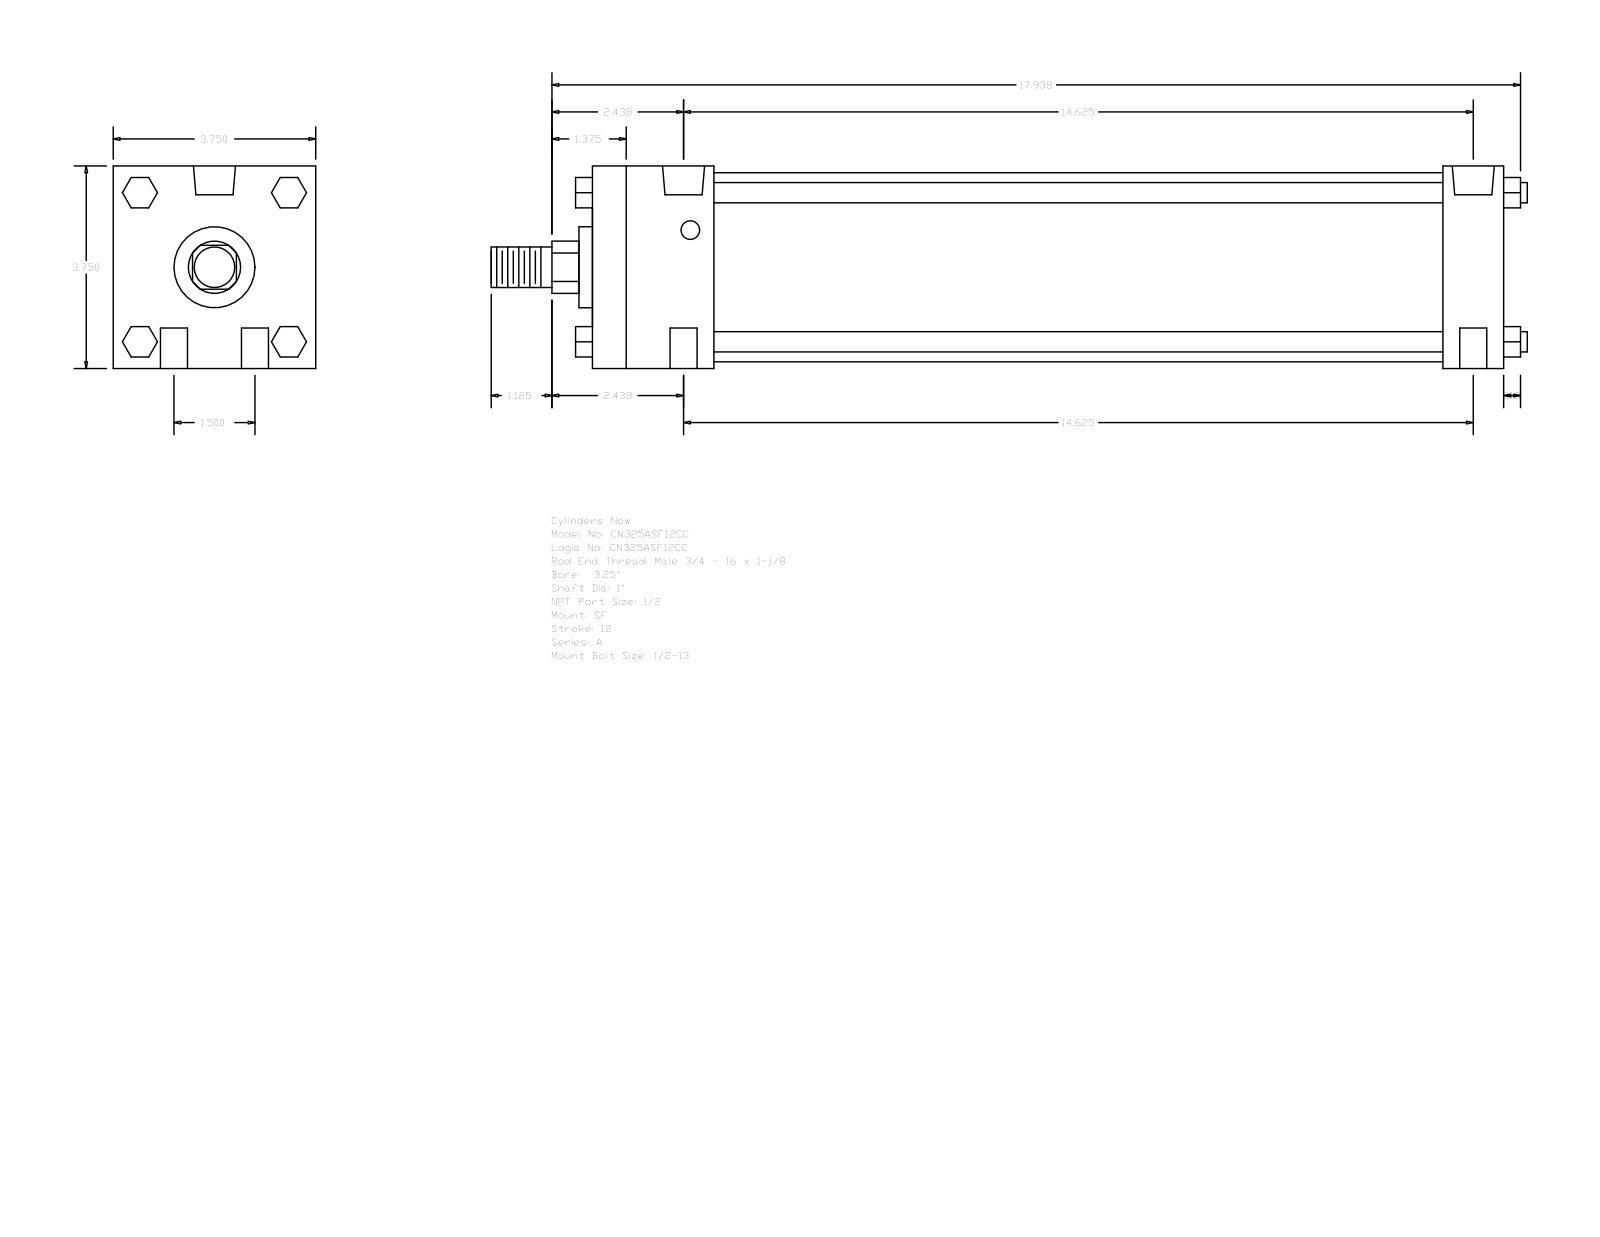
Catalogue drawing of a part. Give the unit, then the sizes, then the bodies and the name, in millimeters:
Units: millimetres
Overall size (bounding box): 487.36 × 95.25 × 95.25
Round holes (diameter × count): ⌀12.7 ×4, ⌀8.73 ×2, ⌀19.77 ×2
Round bosses / shafts (diameter × count): ⌀9.53 ×4, ⌀88.9 ×1, ⌀38.1 ×1, ⌀25.4 ×1, ⌀19.05 ×1
Partial cylindrical surfaces — rounded edges, fillets, slot ends (radius × count): R12.29 ×1
Main face-to-face distances: 95.24, 428.63, 400.05, 28.58, 57.15, 342.9, 371.48, 14.28, 35.05, 60.71
Hole centre spacings: 19.05, 371.97, 371.48, 38.1, 373.43, 365.12
Bodies: 0 solids, 124 faces (94 planar, 30 cylindrical, 0 other)
Part name (STEP PRODUCT): A_SF__0325_1
STEP written by: GSSL Pune (CONFIG_CONTROL_DESIGN)
